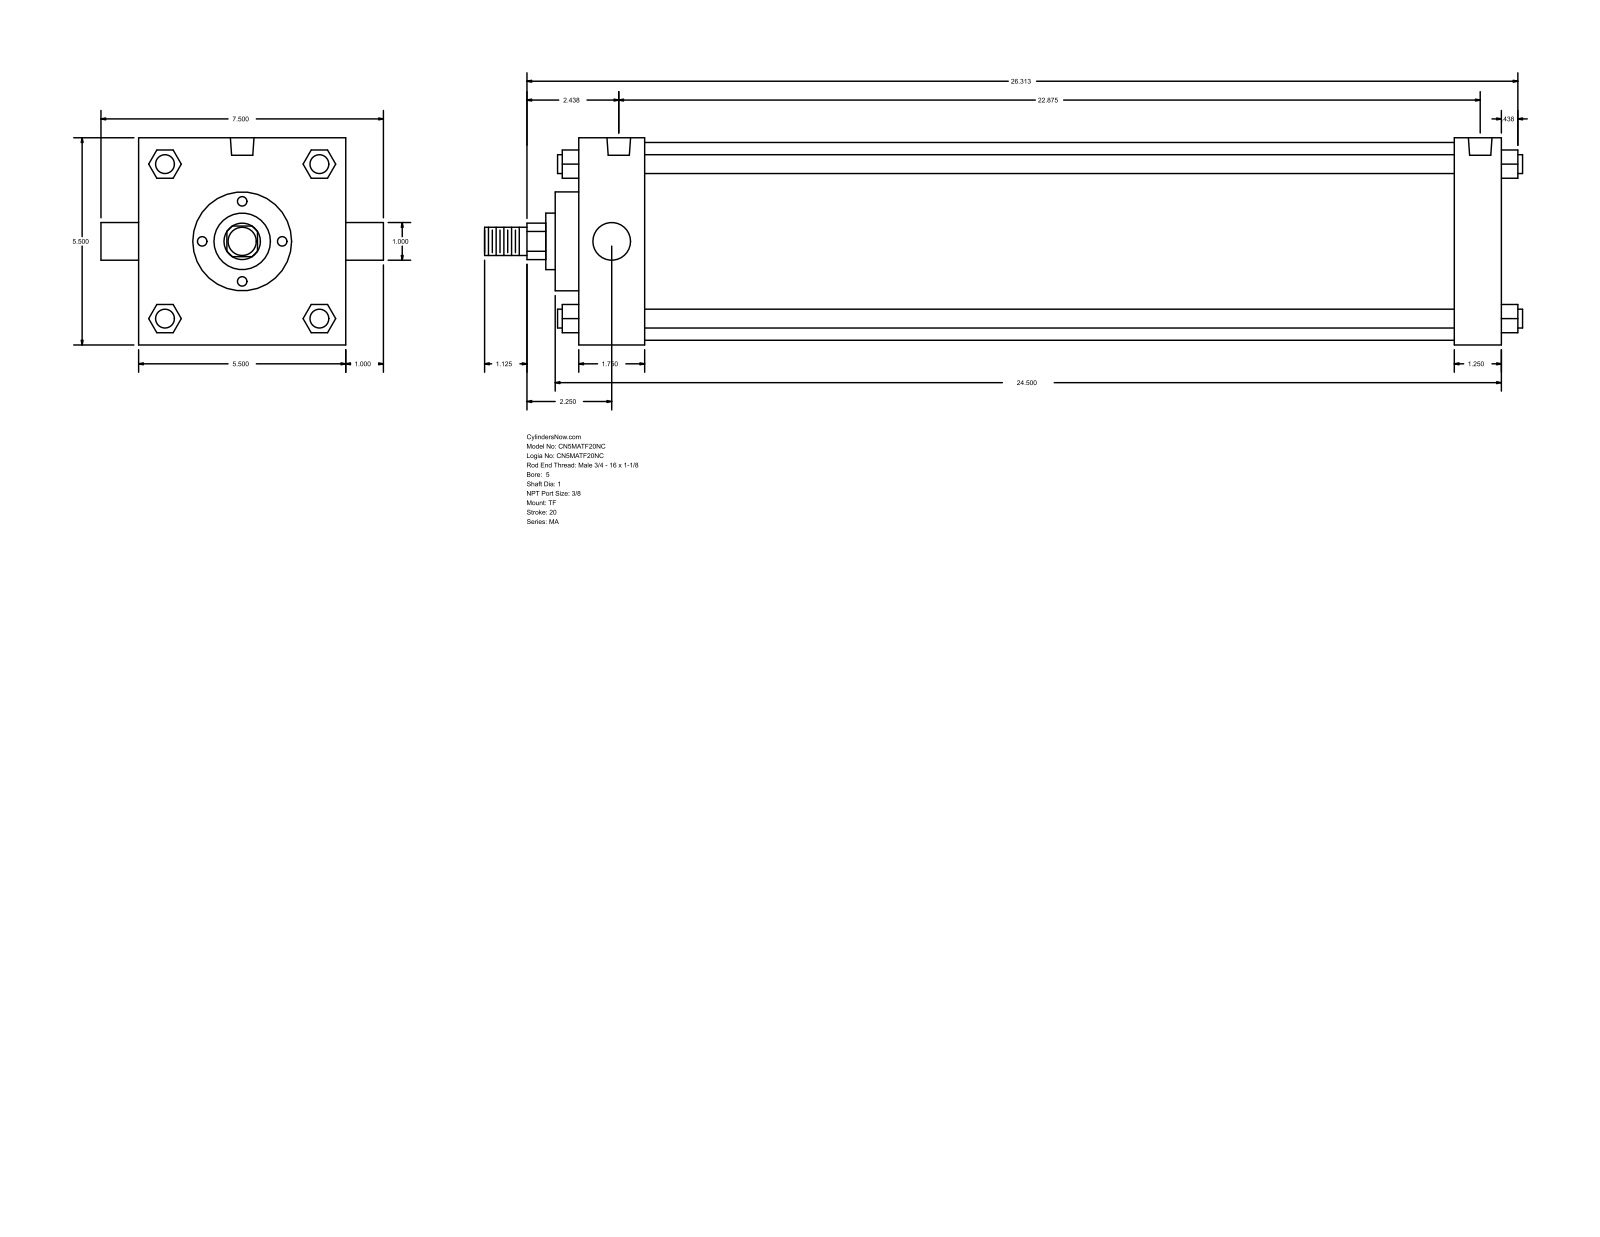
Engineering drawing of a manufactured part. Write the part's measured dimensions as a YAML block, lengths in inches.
part_name: "MA_TF__0500_1"
step_written_by: "GSSL Pune (CONFIG_CONTROL_DESIGN)"
units: inches
bodies: {solids: 0, faces: 122, planar: 93, cylindrical: 29, other: 0}
overall_size: [27.563, 7.5, 5.5]
round_holes:
  - {diameter: 0.437, count: 3}
  - {diameter: 0.627, count: 2}
round_bosses_or_shafts:
  - {diameter: 0.5, count: 4}
  - {diameter: 1, count: 2}
  - {diameter: 5.25, count: 1}
  - {diameter: 2.625, count: 1}
  - {diameter: 1.5, count: 1}
  - {diameter: 0.75, count: 1}
partial_cylinders:
  - {radius: 0.484, count: 1}
face_to_face_distances: [5.5, 24.5, 23.25, 1.25, 1.75, 21.5, 22.75, 0.625, 2.375, 23.875]
hole_center_spacings: [0.187, 0.188, 22.5, 22.687, 22.688, 22.875]
